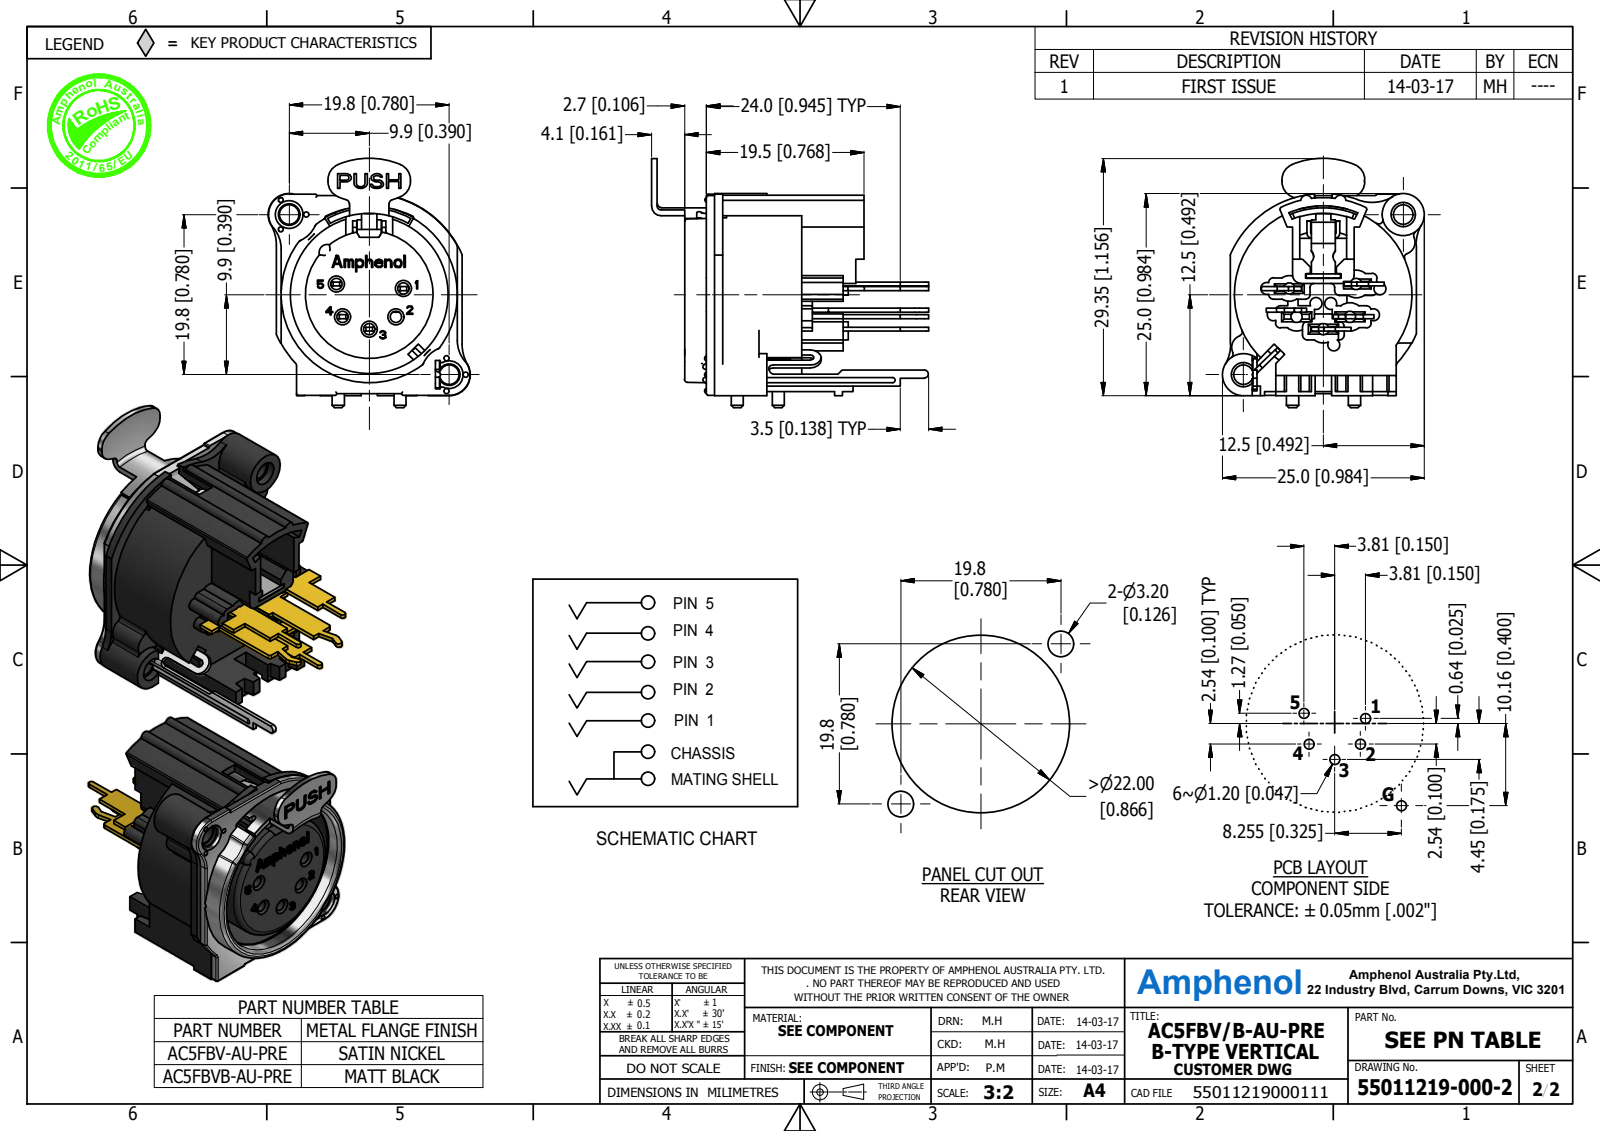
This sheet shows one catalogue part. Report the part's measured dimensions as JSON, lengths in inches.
{"part_name": "AC5FBV-AU-PRE simplified", "step_written_by": "Autodesk Inventor 2023 (AUTOMOTIVE_DESIGN)", "units": "inches", "bodies": {"solids": 1, "faces": 1202, "planar": 933, "cylindrical": 195, "other": 74}, "overall_size": [1.351, 1.215, 0.984], "volume_in3": 0.433, "surface_area_in2": 7.553, "round_holes": [[0.055, 5], [0.094, 2], [0.106, 2], [0.047, 1], [0.118, 1], [0.134, 1], [0.768, 1], [0.813, 1]], "round_bosses_or_shafts": [[0.059, 4], [0.047, 2], [0.795, 1], [0.622, 1], [0.205, 1]], "partial_cylinders_radius": [[0.008, 35], [0.02, 17], [0.012, 12], [0.024, 12], [0.016, 6], [0.03, 5], [0.039, 5], [0.079, 4]], "face_to_face_distances": [0.039, 0.425, 0.134, 0.02, 0.689, 0.264, 0.465, 0.079, 0.559, 0.728], "hole_center_spacings": [0.169, 0.143, 0.168, 0.551, 0.143, 0.163, 0.259, 0.26]}
